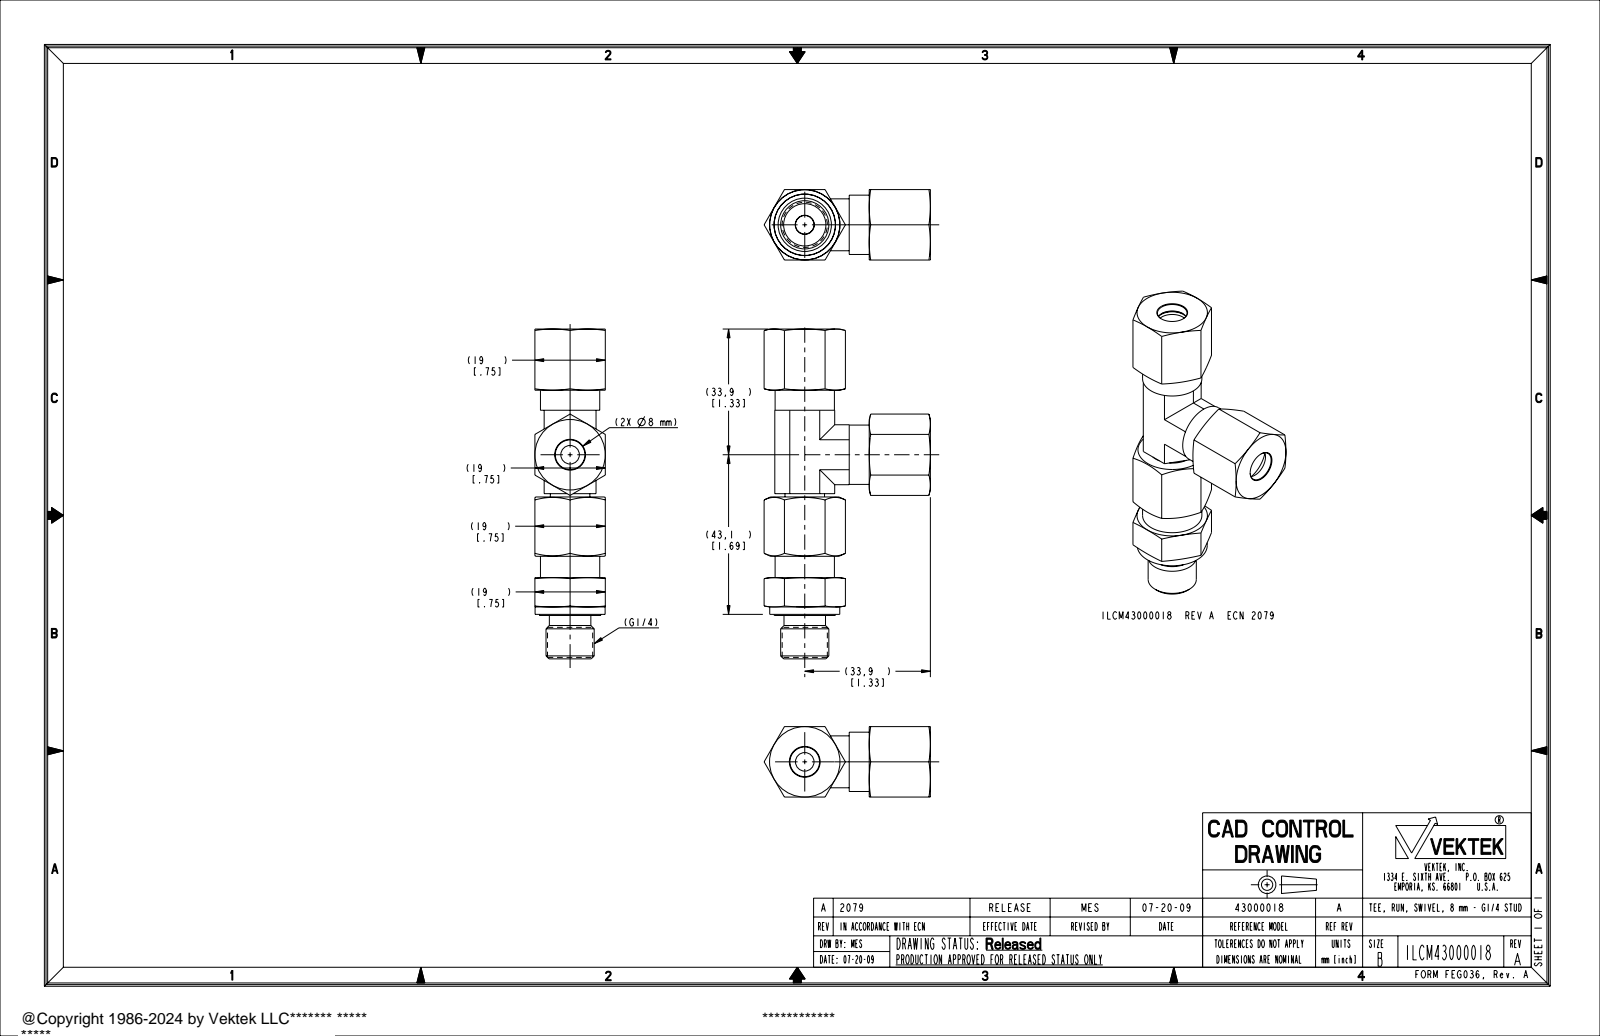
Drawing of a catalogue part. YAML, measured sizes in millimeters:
part_name: "ILCM43000018"
step_written_by: "PRO/ENGINEER BY PARAMETRIC TECHNOLOGY CORPORATION, 2007460 (AUTOMOTIVE_DESIGN_CC2)"
units: millimeters
bodies: {solids: 1, faces: 227, planar: 87, cylindrical: 54, other: 86}
overall_size: [89, 44.9, 19]
volume: 22650
surface_area: 12790
round_holes:
  - {diameter: 5, count: 2}
  - {diameter: 8, count: 2}
  - {diameter: 14.4, count: 2}
  - {diameter: 11.6, count: 1}
  - {diameter: 12.5, count: 1}
  - {diameter: 14.5, count: 1}
  - {diameter: 16.6, count: 1}
round_bosses_or_shafts:
  - {diameter: 16, count: 2}
  - {diameter: 18.9, count: 1}
  - {diameter: 16.5, count: 1}
  - {diameter: 13, count: 1}
  - {diameter: 12.2, count: 1}
  - {diameter: 11.2, count: 1}
  - {diameter: 11, count: 1}
  - {diameter: 10.7, count: 1}
face_to_face_distances: [19, 16.5, 2.5, 14, 9.9, 21.9, 12, 67.1, 6.6, 45.3]
